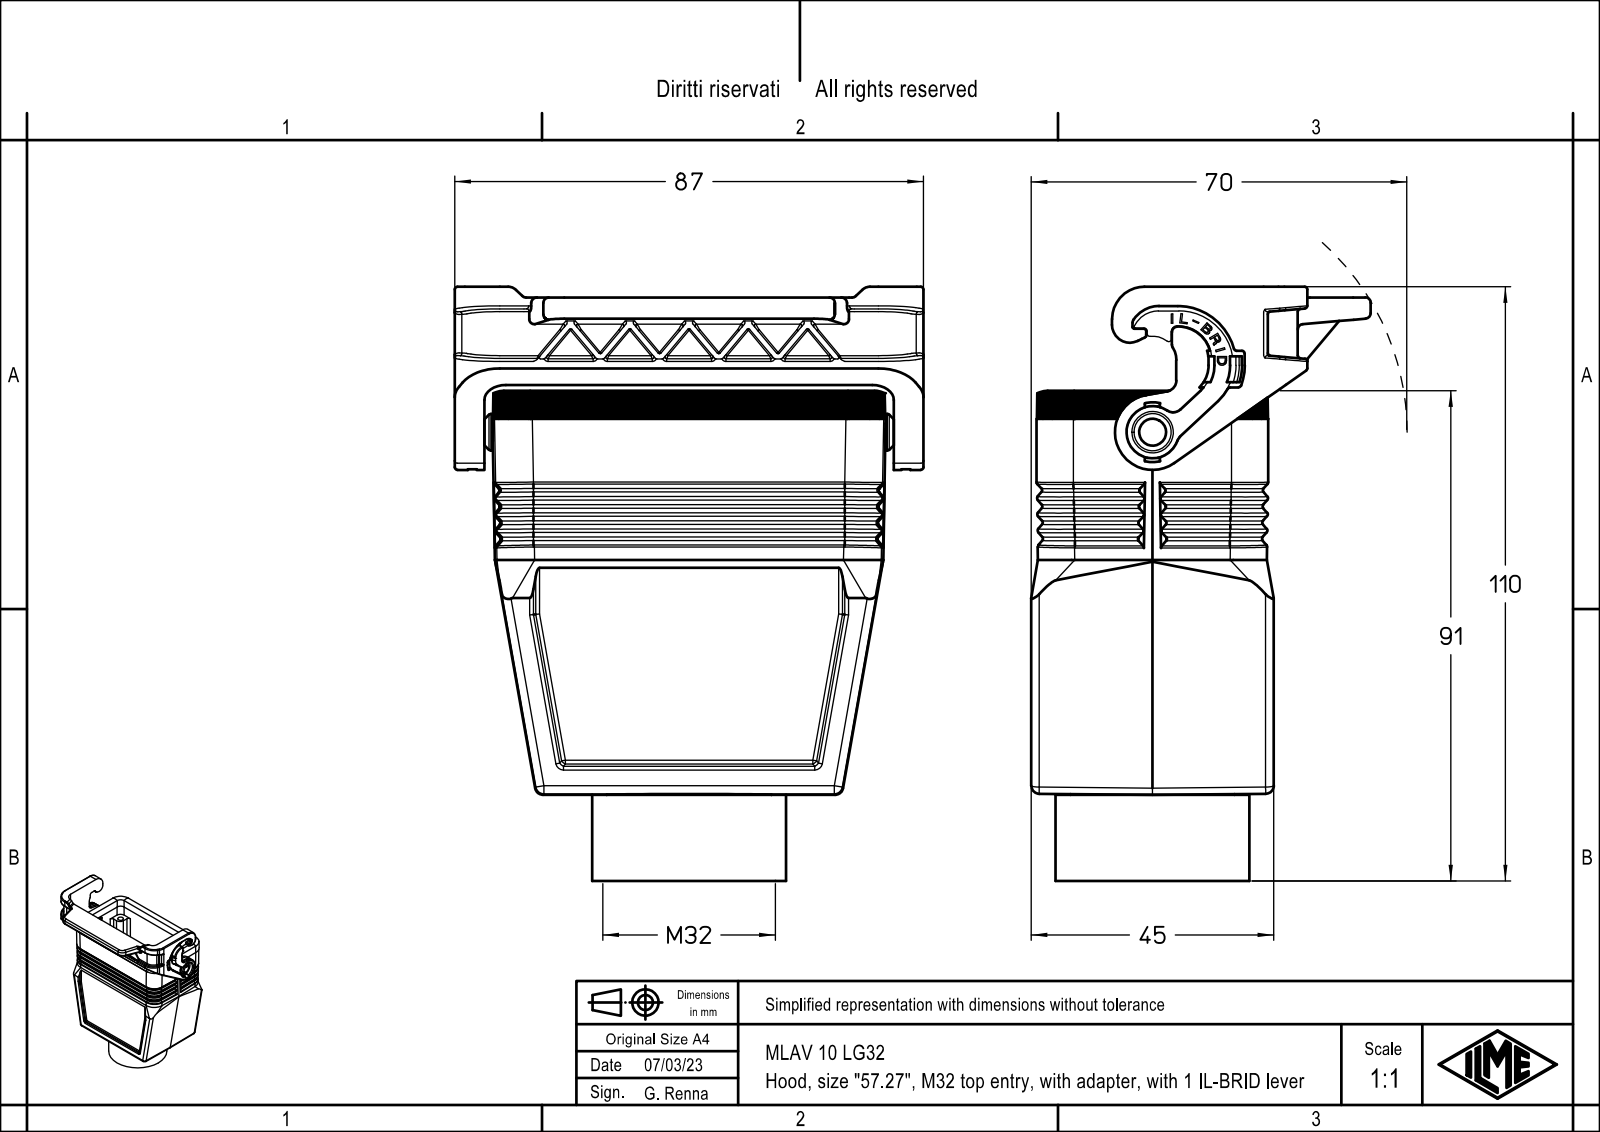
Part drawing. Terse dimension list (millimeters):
name: MLAV 10 LG32
written by: Creo Elements/Direct Modeling 20.1B 02-Apr-2019 (C) Parametric Technology GmbH (AUTOMOTIVE_DESIGN)
unit: mm
bodies: 1 solid, 1272 faces (713 planar, 315 cylindrical, 244 other)
size: 110.25 × 87 × 63
volume: 92 775 mm³; area: 50 854 mm²
holes: 4× ⌀3, 4× ⌀3.5, 1× ⌀3.25, 1× ⌀5.4, 1× ⌀7.7, 1× ⌀27, 1× ⌀30.6
bosses: 1× ⌀36, 1× ⌀32, 1× ⌀30.5, 1× ⌀6.9, 1× ⌀6.8, 1× ⌀5.2, 1× ⌀3.2
rounds: 27× R0.1, 25× R0.5, 25× R1.5, 15× R0.2, 14× R1, 14× R7, 13× R0.33, 12× R3
face distances: 39.25, 3.75, 1, 43, 4.75, 7, 2, 34.5, 38.25, 35.5
hole spacings: 31.54, 27, 57, 63.07
